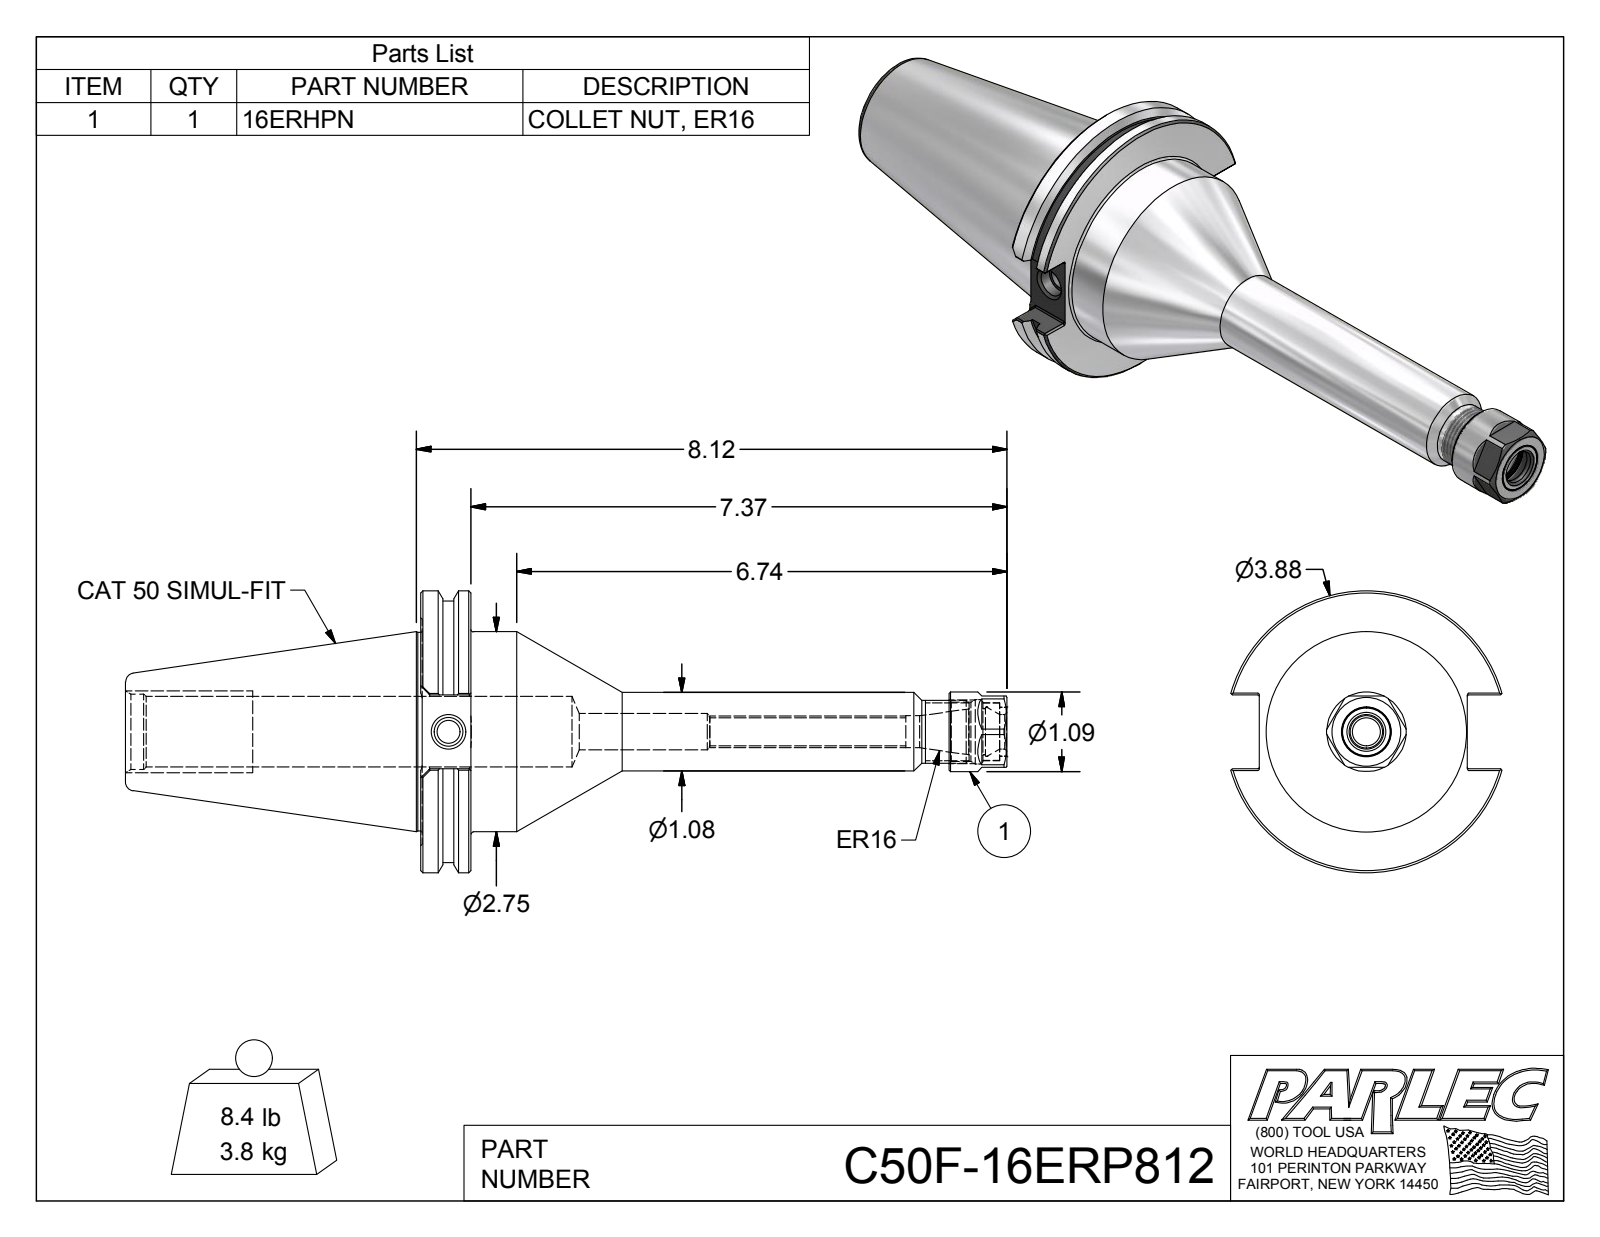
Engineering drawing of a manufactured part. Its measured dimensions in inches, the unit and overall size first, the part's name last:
Units: inches
Overall size (bounding box): 12.12 × 3.875 × 3.729
Round holes (diameter × count): ⌀0.315 ×1, ⌀0.383 ×1, ⌀0.399 ×1, ⌀0.44 ×1, ⌀0.474 ×1, ⌀0.5 ×1, ⌀0.63 ×1, ⌀0.674 ×1, ⌀0.68 ×1, ⌀0.794 ×1, ⌀0.814 ×1, ⌀0.883 ×1
Round bosses / shafts (diameter × count): ⌀3.875 ×1, ⌀3.594 ×1, ⌀2.75 ×1, ⌀2.73 ×1, ⌀1.092 ×1, ⌀1.08 ×1, ⌀0.866 ×1, ⌀0.79 ×1
Partial cylindrical surfaces — rounded edges, fillets, slot ends (radius × count): R0.02 ×12
Main face-to-face distances: 0.691, 0.02, 0.671, 4.059, 4.079, 4.75, 2.86, 0.98, 12.12, 8.061
Volume: 29.73 in³ · Surface area: 116.1 in²
Bodies: 3 solids, 136 faces (54 planar, 39 cylindrical, 43 other)
Part name (STEP PRODUCT): C50F-16ERP812; C50F-16ER8-1; 16ERHPN
STEP written by: Autodesk Inventor 2012 (AUTOMOTIVE_DESIGN)
